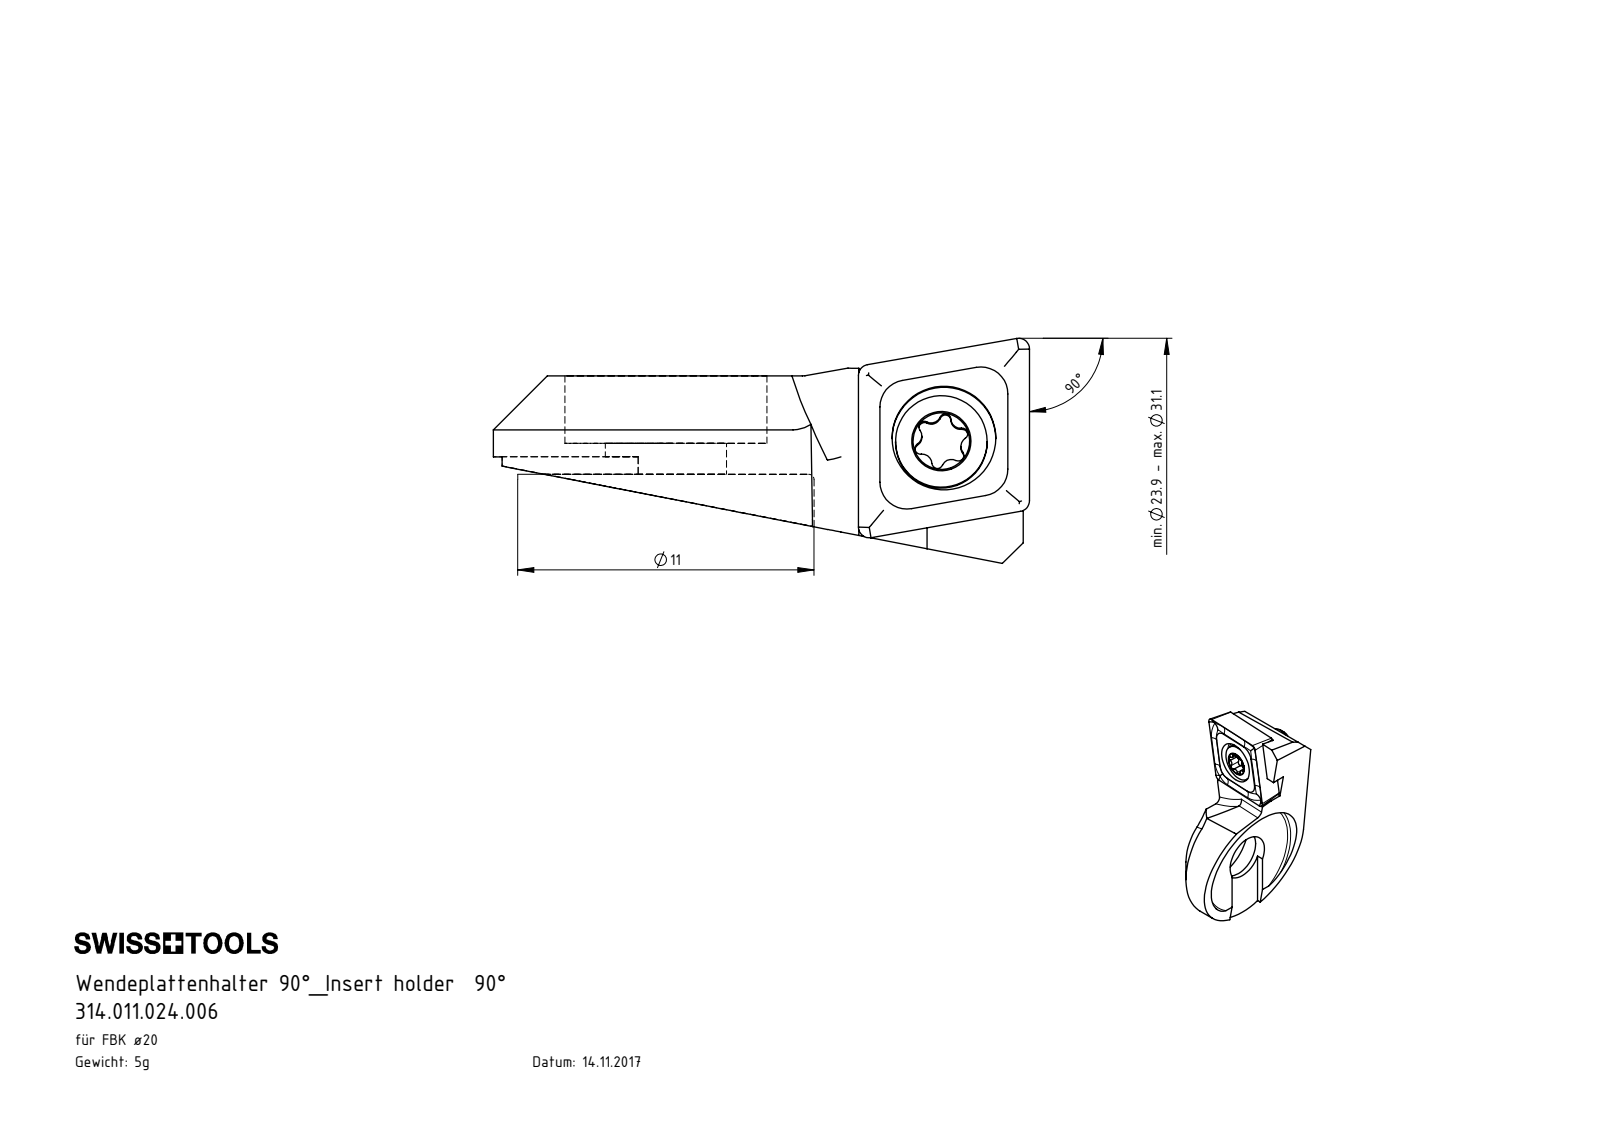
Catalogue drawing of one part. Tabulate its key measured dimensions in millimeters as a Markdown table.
| quantity | value |
| --- | --- |
| part name | F20-WCA.001.005_D_fertigbearbeitet; CCMT060204; WCA-ER2.001.006_A; 314.011.024.006 |
| STEP written by | SolidWorks 2017 (CONFIG_CONTROL_DESIGN) |
| units | millimeters |
| bodies | 3 solids, 131 faces (40 planar, 42 cylindrical, 49 other) |
| overall size | 19.9 × 12.8 × 8.36 |
| volume | 557 mm³ |
| surface area | 853 mm² |
| round holes (diameter × count) | 2.05 × 1, 2.8 × 1, 3.85 × 1, 4.5 × 1, 7.5 × 1 |
| round bosses / shafts (diameter × count) | 3.4 × 1, 2.5 × 1 |
| partial cylindrical surfaces (radius × count) | 0.21 × 6, 0.36 × 5, 0.5 × 2, 5 × 2, 0.36 × 1, 5.5 × 1, 6.4 × 1, 10 × 1 |
| main face-to-face distances | 1.15, 2.5, 3.65, 3, 0.5, 0.65, 2.38, 2.28, 1.08, 0.98 |
